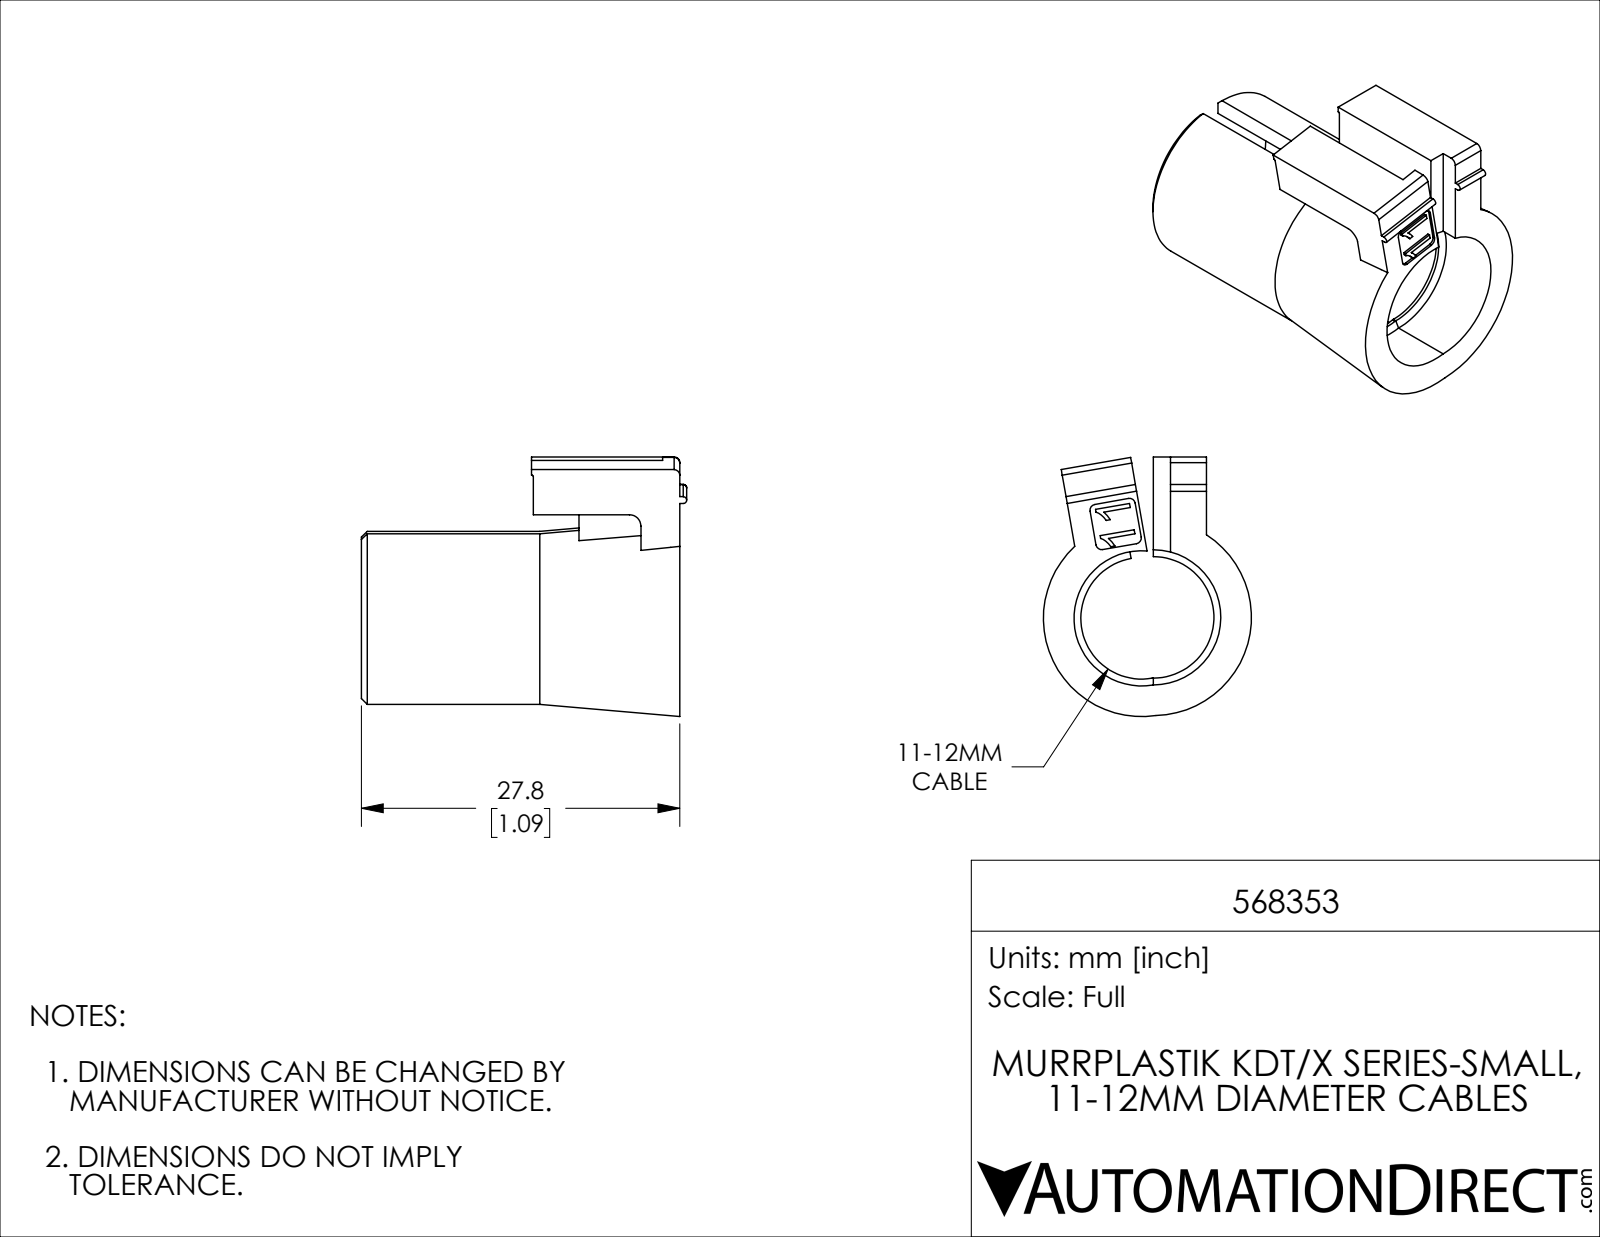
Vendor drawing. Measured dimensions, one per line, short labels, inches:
name: 568353
written by: SolidWorks 2019 (CONFIG_CONTROL_DESIGN)
unit: in
bodies: 1 solid, 91 faces (50 planar, 25 cylindrical, 16 other)
size: 1.118 × 0.892 × 0.715
volume: 0.171 in³; area: 4.995 in²
rounds: 6× R0.02, 2× R0.004, 2× R0.012, 2× R0.039, 2× R0.209, 2× R0.232, 2× R0.295
face distances: 0.157, 0.183, 0.183, 1.094, 0.059, 0.504, 0.591, 0.445, 1.035, 0.346
